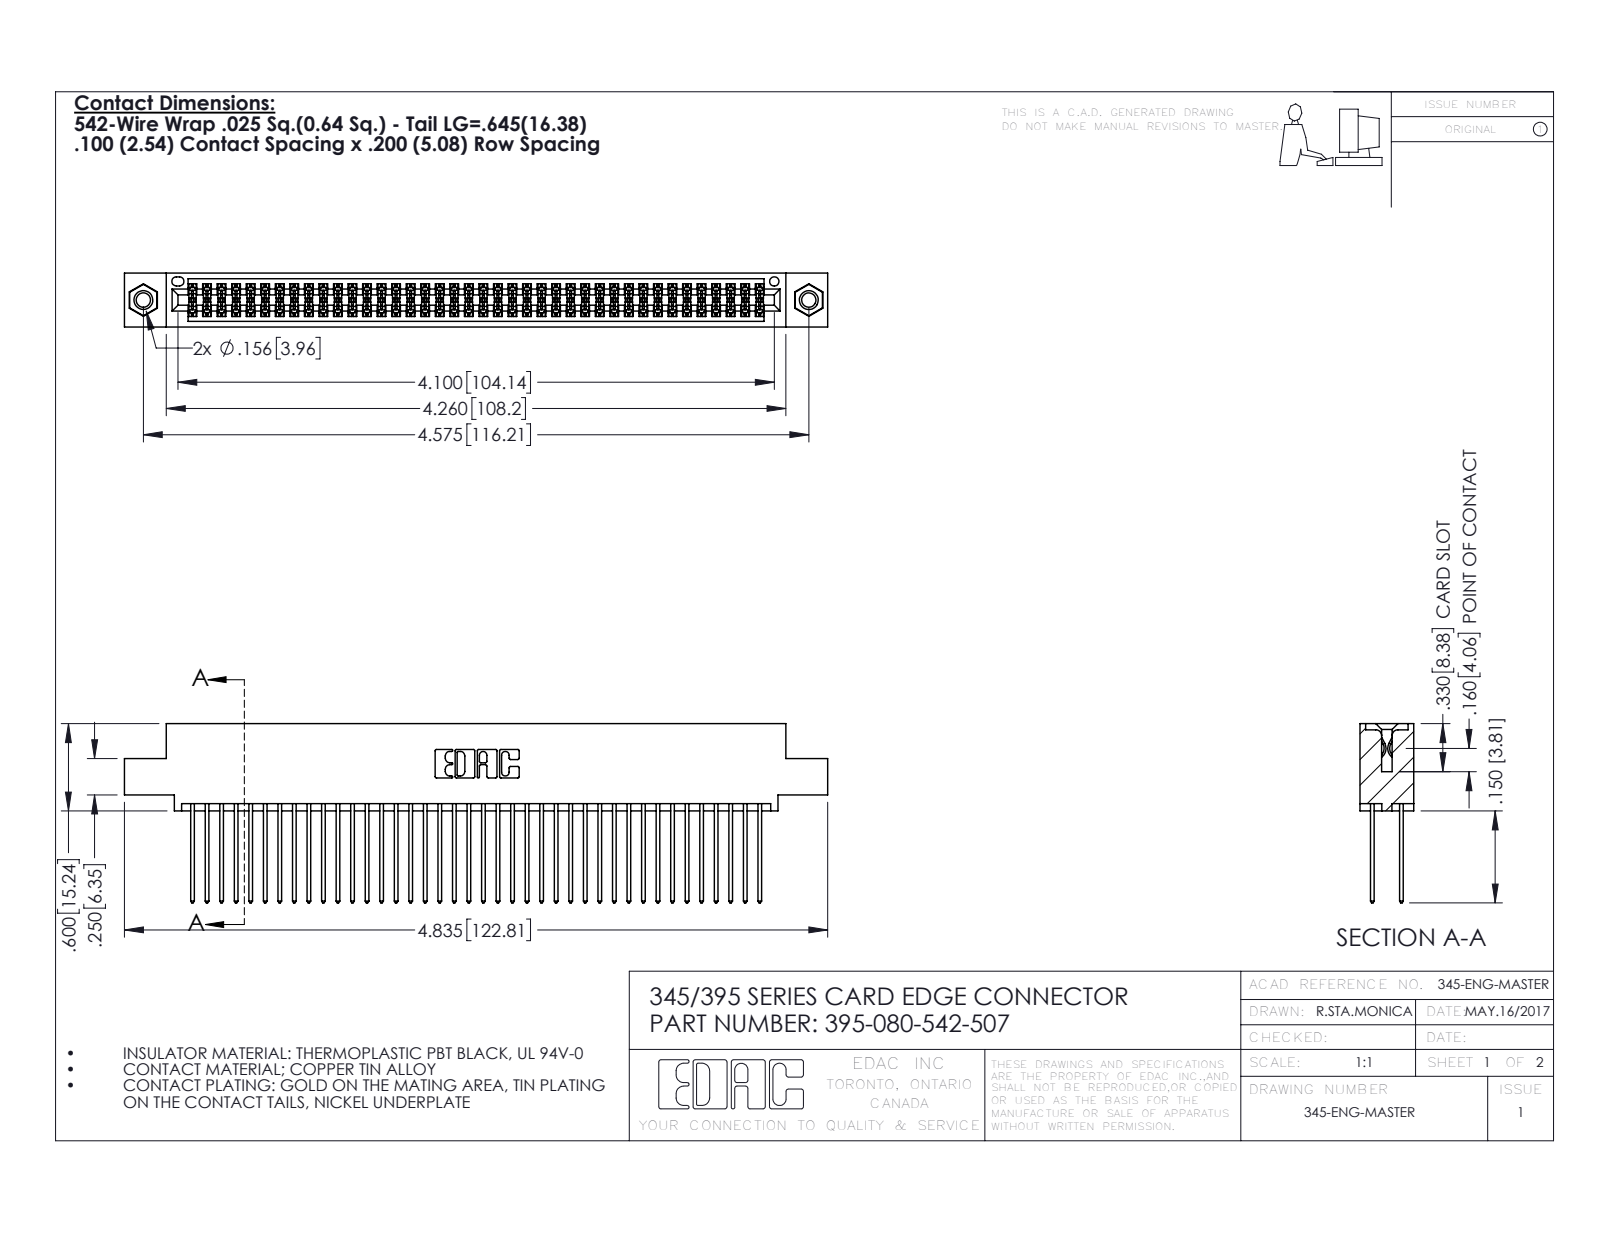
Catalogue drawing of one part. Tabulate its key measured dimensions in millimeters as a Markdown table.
| quantity | value |
| --- | --- |
| part name | 395-080-542-507; 345 Part_0.110 Offset - 0.156 Dia-TI; 345-292-001_345-293-142; 345-250-001_345-250-005-103 |
| STEP written by | SolidWorks 2016 (CONFIG_CONTROL_DESIGN) |
| units | millimeters |
| bodies | 83 solids, 4190 faces (2756 planar, 1418 cylindrical, 16 other) |
| overall size | 122.8 × 31.3 × 9.4 |
| volume | 12 200 mm³ |
| surface area | 19 850 mm² |
| round holes (diameter × count) | 2.5 × 2, 3.2 × 2, 4 × 2, 1.6 × 1 |
| round bosses / shafts (diameter × count) | 3.9 × 2 |
| partial cylindrical surfaces (radius × count) | 0.2 × 120, 0.3 × 80, 0.3 × 22, 0.2 × 6, 0.8 × 6, 0.7 × 3, 0.4 × 2, 0.5 × 2 |
| main face-to-face distances | 1.8, 7.6, 5.1, 2.5, 6.9, 0.6, 5.7, 9.4, 4.4, 3.8 |
| hole center spacings | 6.9, 110.2, 116.2 |
